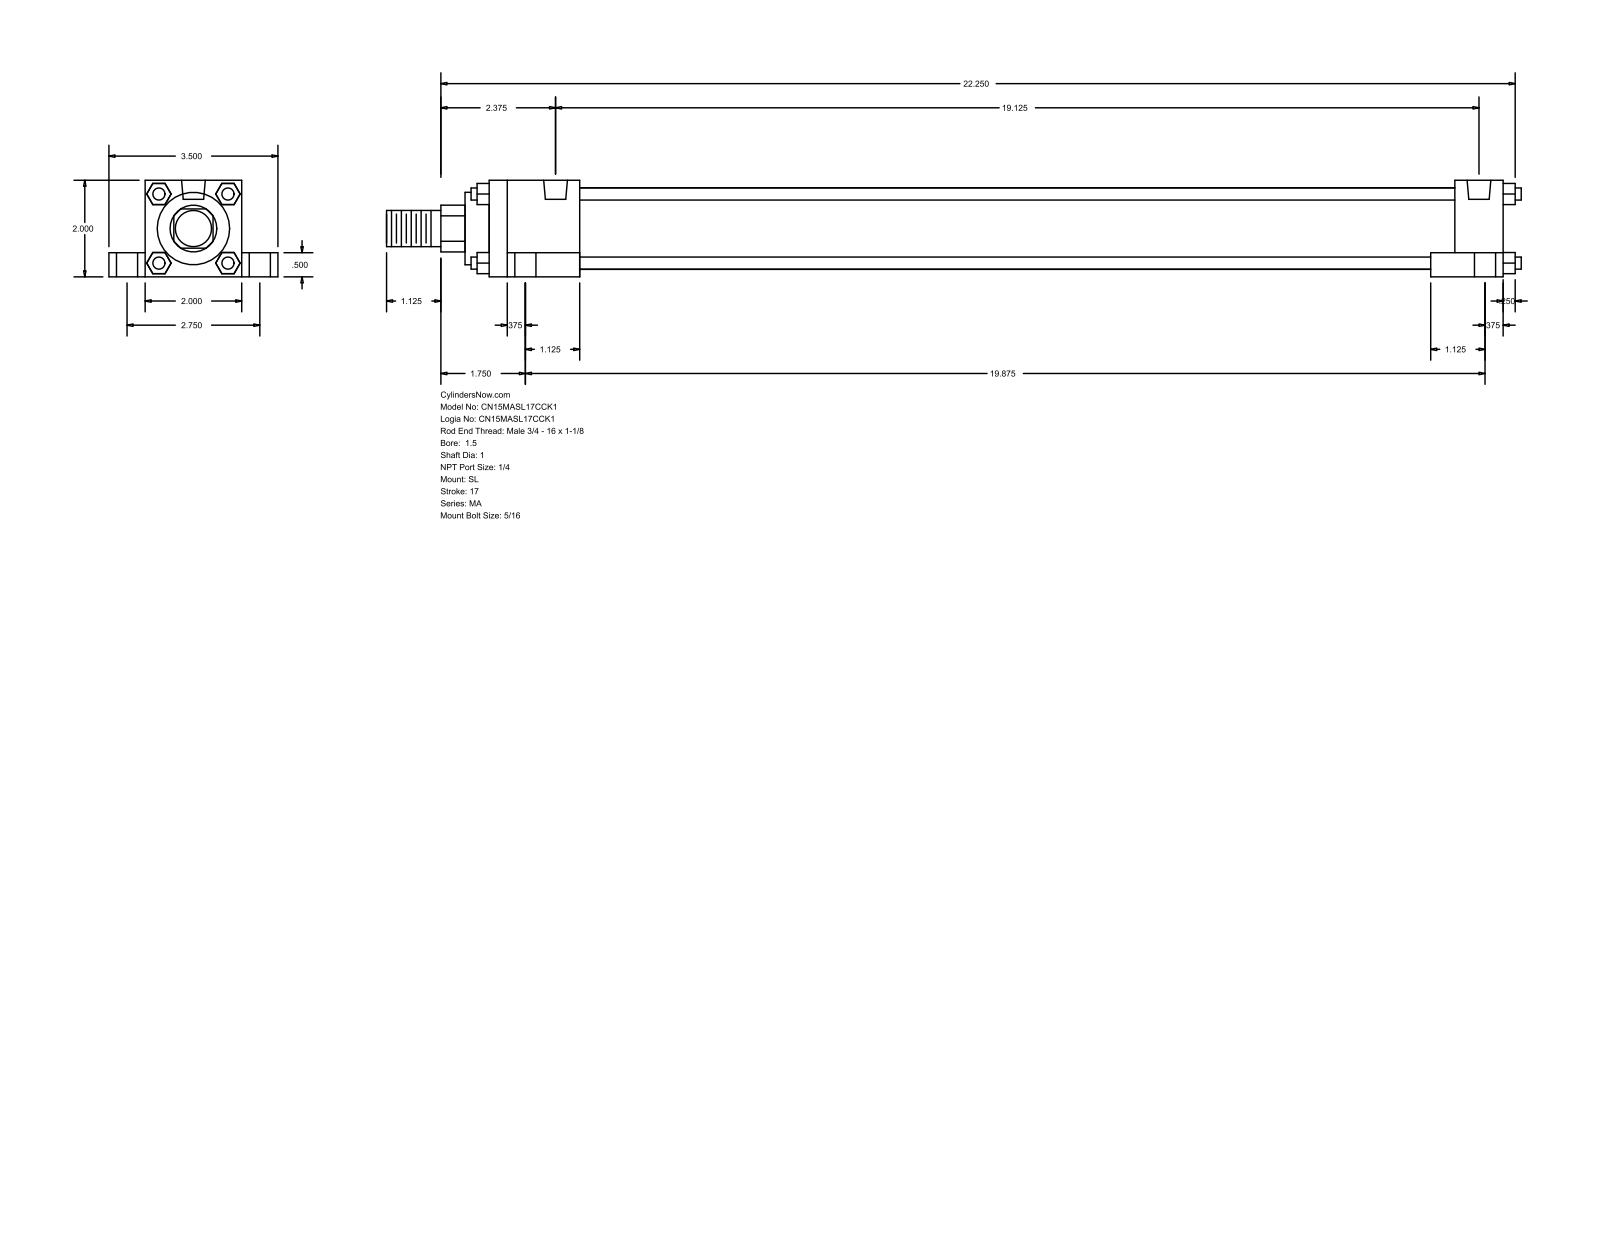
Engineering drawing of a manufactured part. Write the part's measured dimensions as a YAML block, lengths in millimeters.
part_name: "MA_SL__0150_1"
step_written_by: "GSSL Pune (CONFIG_CONTROL_DESIGN)"
units: millimeters
bodies: {solids: 0, faces: 148, planar: 112, cylindrical: 36, other: 0}
overall_size: [596.9, 88.9, 50.8]
round_holes:
  - {diameter: 7.94, count: 4}
  - {diameter: 11.11, count: 4}
  - {diameter: 17.46, count: 4}
  - {diameter: 12.49, count: 2}
round_bosses_or_shafts:
  - {diameter: 6.35, count: 4}
  - {diameter: 42.93, count: 1}
  - {diameter: 38.1, count: 1}
  - {diameter: 25.4, count: 1}
  - {diameter: 19.05, count: 1}
partial_cylinders:
  - {radius: 12.29, count: 1}
face_to_face_distances: [50.8, 12.7, 19.05, 69.85, 38.1, 9.52, 533.4, 25.4, 6.35, 508]
hole_center_spacings: [35.06, 38.36, 69.84, 485.77, 490.19, 502.86, 504.82, 509.63]
